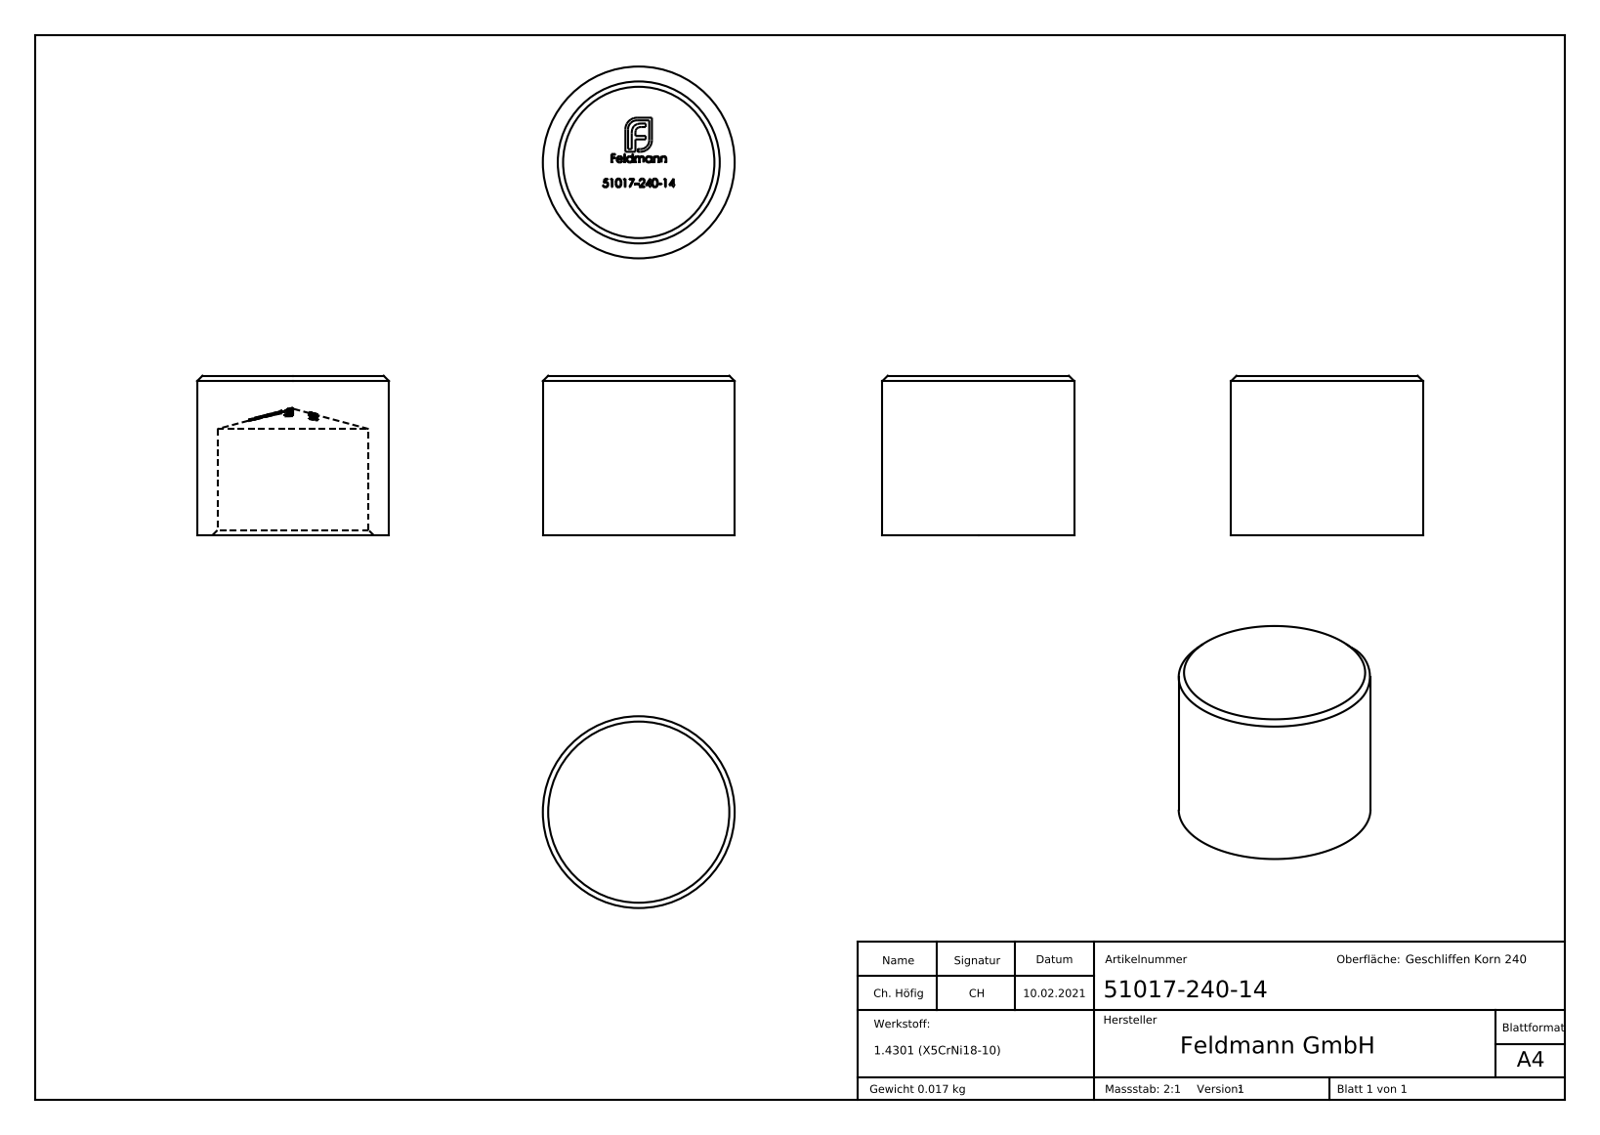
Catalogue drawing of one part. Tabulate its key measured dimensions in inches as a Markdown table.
| quantity | value |
| --- | --- |
| part name | 51017-240-14 |
| STEP written by | SolidWorks 2018 (CONFIG_CONTROL_DESIGN) |
| units | inches |
| bodies | 1 solid, 291 faces (146 planar, 4 cylindrical, 141 other) |
| overall size | 0.709 × 0.709 × 0.591 |
| volume | 0.129 in³ |
| surface area | 2.771 in² |
| round holes (diameter × count) | 0.559 × 1 |
| round bosses / shafts (diameter × count) | 0.709 × 1 |
| main face-to-face distances | 0.591, 0.088, 0.074, 0.078, 0.028, 0.048, 0.021, 0.051, 0.098, 0.013 |
